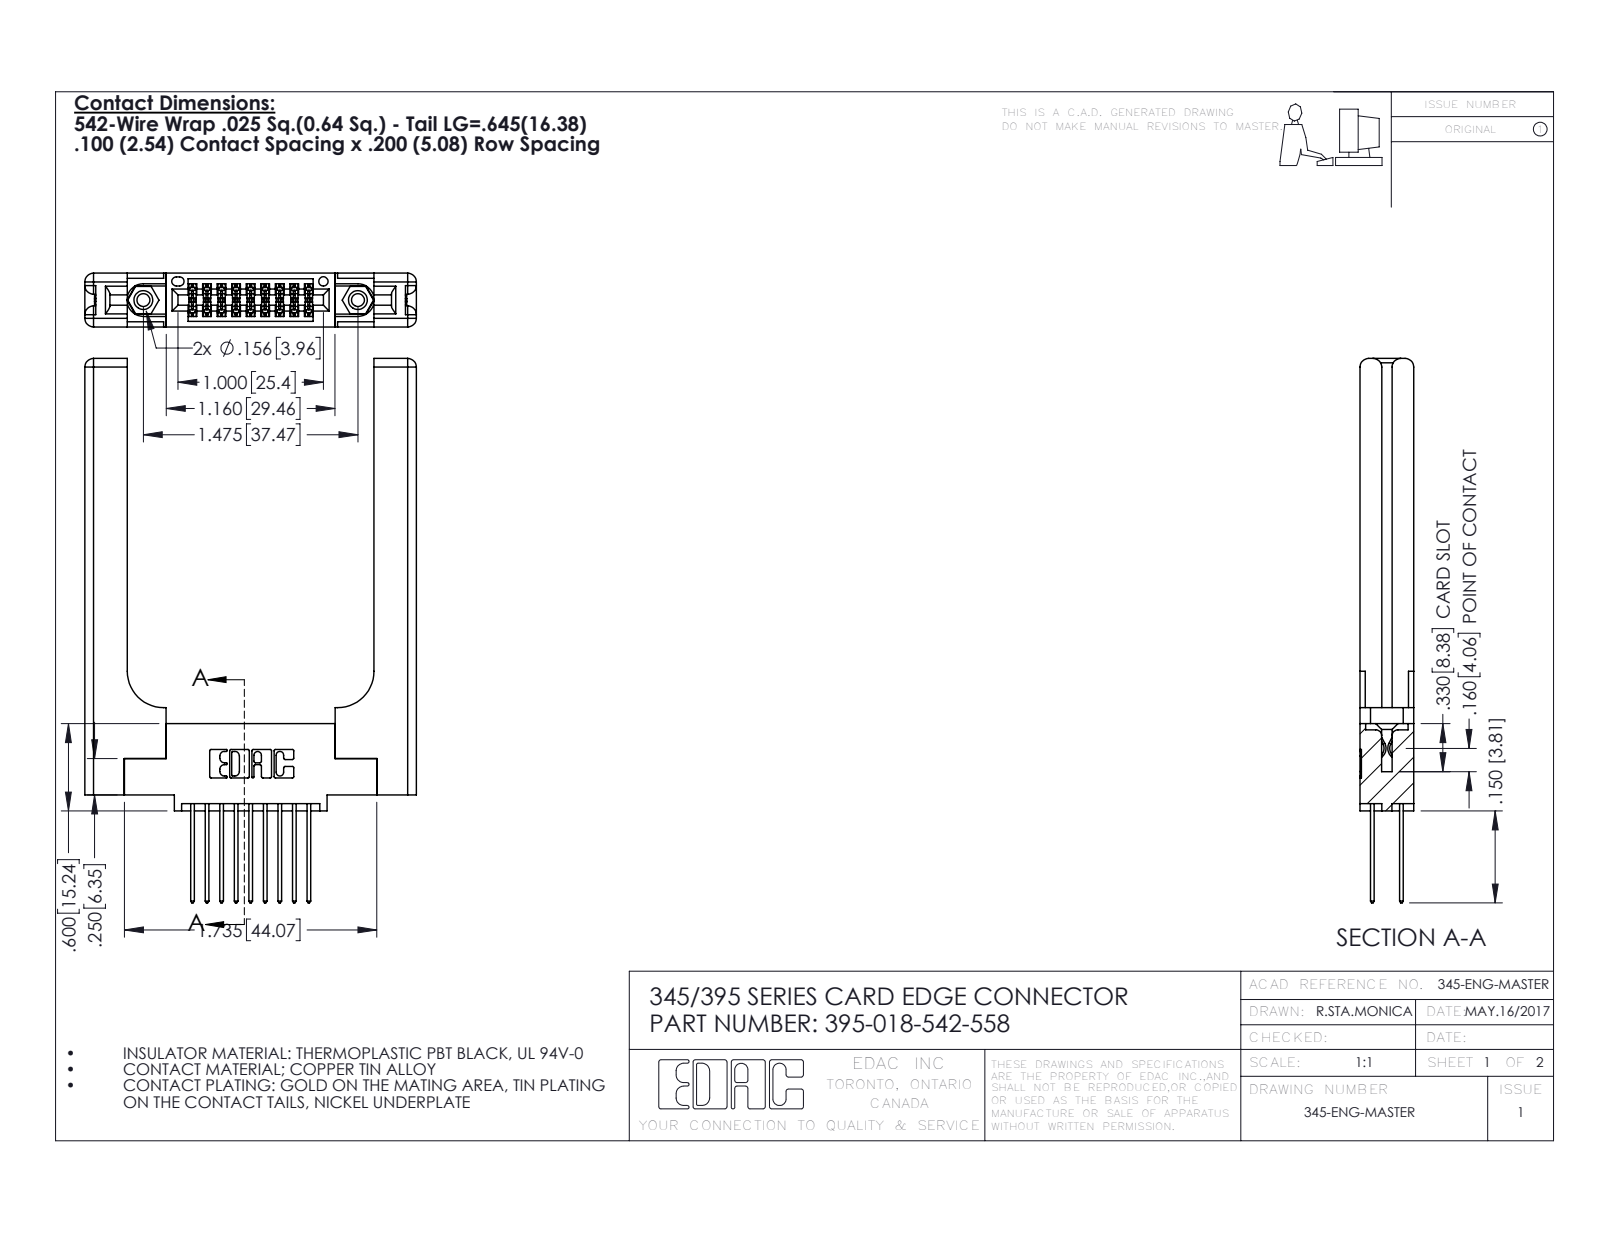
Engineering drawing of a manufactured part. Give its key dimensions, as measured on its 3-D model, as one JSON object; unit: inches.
{"part_name": "345-250-001_345-250-001-102; 345 Part_0.110 Offset - 0.156 Dia-TH; 395-018-542-558; 345-220-058_345-220-058 (+1 more)", "step_written_by": "SolidWorks 2016 (CONFIG_CONTROL_DESIGN)", "units": "inches", "bodies": {"solids": 23, "faces": 1286, "planar": 826, "cylindrical": 400, "other": 60}, "overall_size": [3.742, 2.279, 0.37], "volume_in3": 0.842, "surface_area_in2": 19.81, "round_holes": [[0.089, 2], [0.125, 2], [0.156, 2], [0.064, 1]], "round_bosses_or_shafts": [[0.155, 2]], "partial_cylinders_radius": [[0.006, 27], [0.01, 22], [0.01, 18], [0.06, 16], [0.007, 6], [0.031, 6], [0.026, 3], [0.014, 2]], "face_to_face_distances": [0.37, 0.072, 0.298, 0.15, 0.077, 0.148, 0.22, 0.225, 0.098, 0.272], "hole_center_spacings": [0.27, 1.244, 1.475]}
